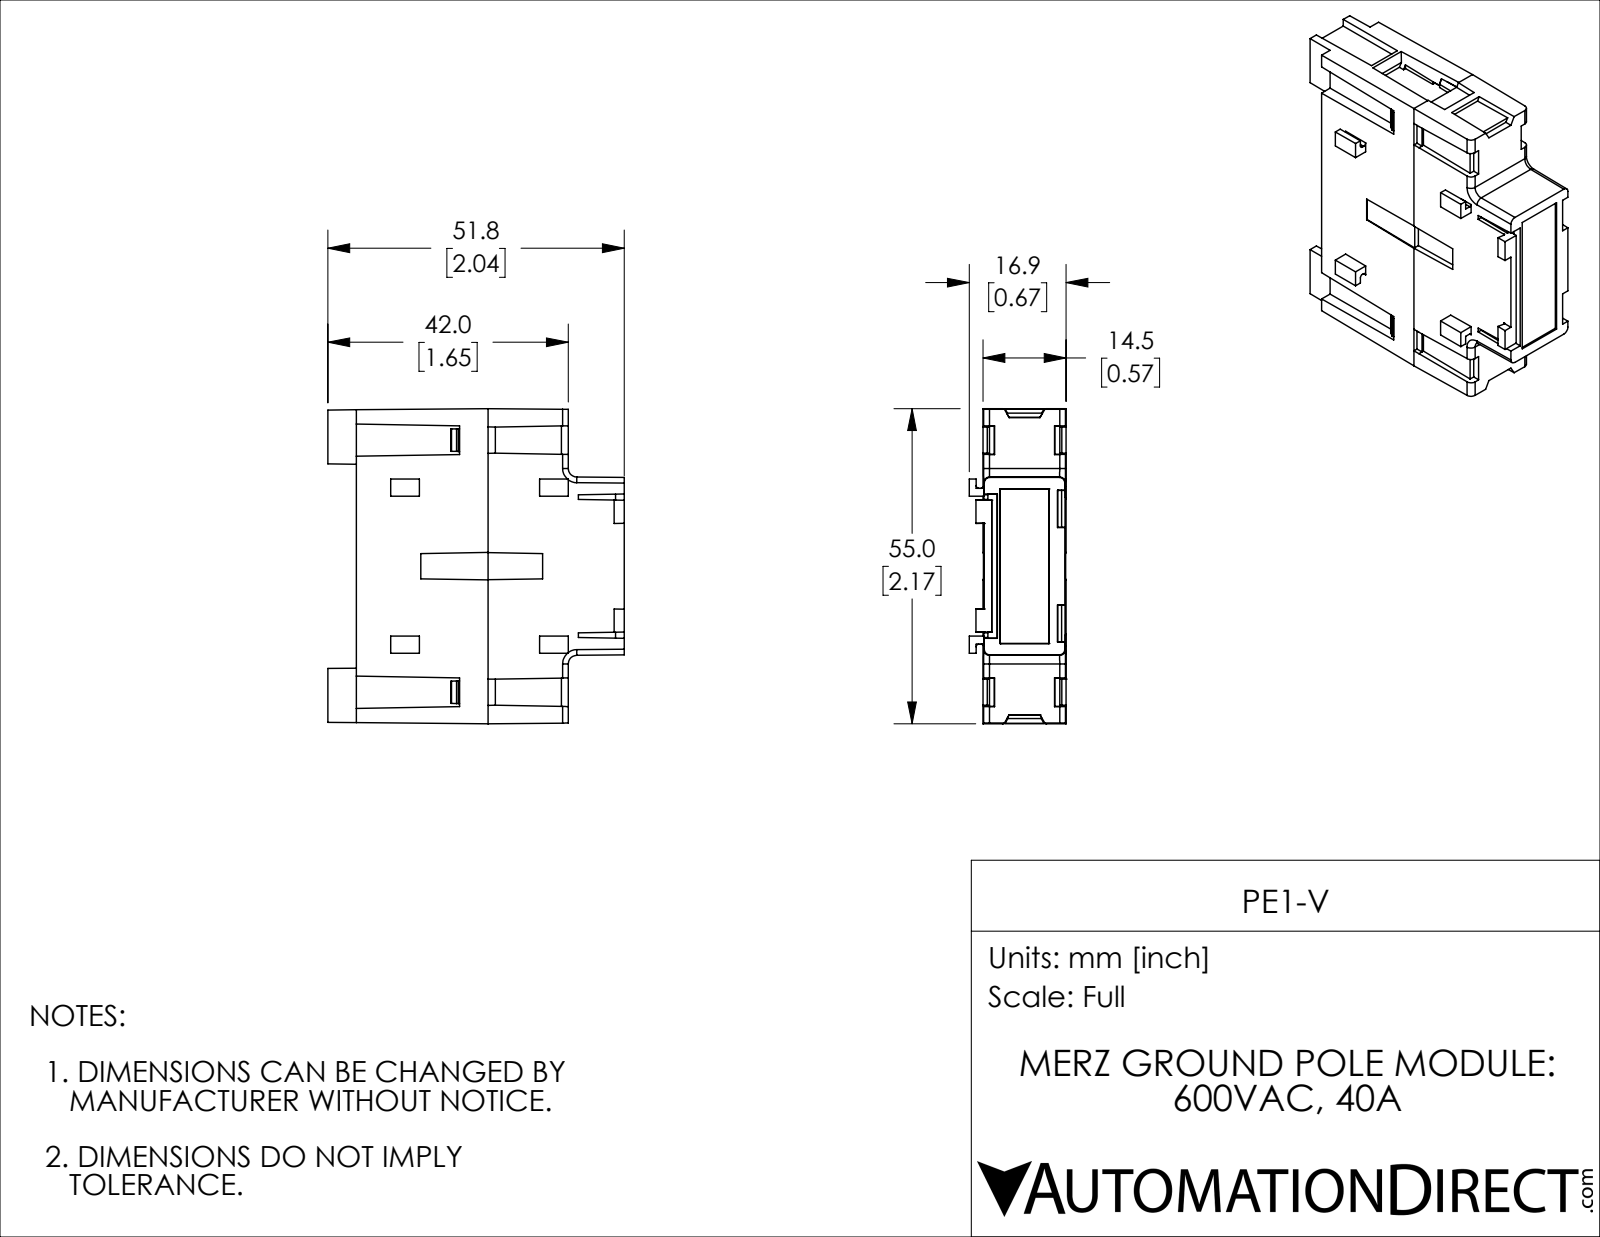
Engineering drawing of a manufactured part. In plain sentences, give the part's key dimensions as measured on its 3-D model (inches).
The part is named "PE1-V". Its 3-D file was written by "SolidWorks 2019 (AUTOMOTIVE_DESIGN)". It is 1 solid with 504 faces: 464 planar, 32 cylindrical and 8 other. Overall it measures 2.165 by 2.037 by 0.665 inches. Its volume is 1.888 cubic inches and its surface area 17.56 square inches. Partial cylindrical surfaces (rounded edges, fillets, slot ends): 6 of radius 0.039, 5 of radius 0.008, 4 of radius 0.02, 2 of radius 0.012, 2 of radius 0.059. The main face-to-face distances are 0.571, 0.044, 1.829, 0.113, 0.37, 0.406, 0.257, 0.372, 1.457, 0.465.
